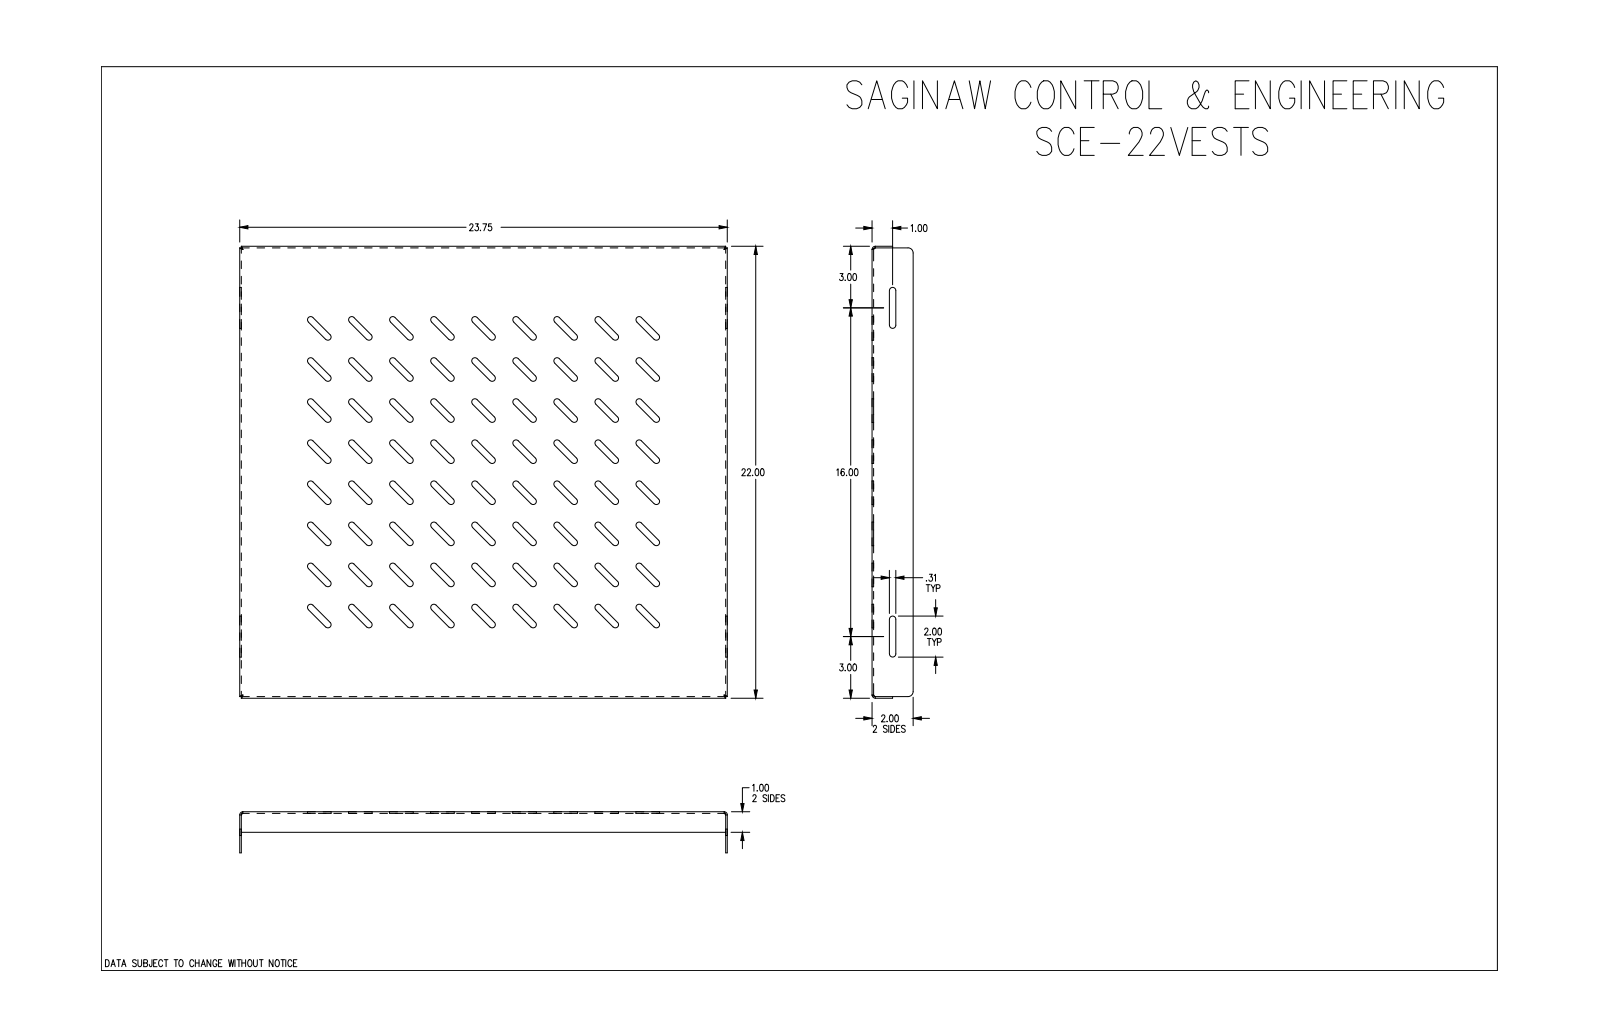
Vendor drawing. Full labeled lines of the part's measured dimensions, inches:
Part name (STEP PRODUCT): SCE-22VESTS
STEP written by: SolidWorks 2019 (CONFIG_CONTROL_DESIGN)
Units: inches
Bodies: 1 solid, 350 faces (174 planar, 168 cylindrical, 8 other)
Overall size (bounding box): 23.75 × 22 × 2
Volume: 47.63 in³ · Surface area: 1 250 in²
Partial cylindrical surfaces — rounded edges, fillets, slot ends (radius × count): R0.156 ×148, R0.078 ×4, R0.156 ×4, R0.02 ×2, R0.25 ×2
Main face-to-face distances: 0.078, 23.672, 21.922, 23.594, 23.75, 21.844, 22, 1, 2.828, 1.414
